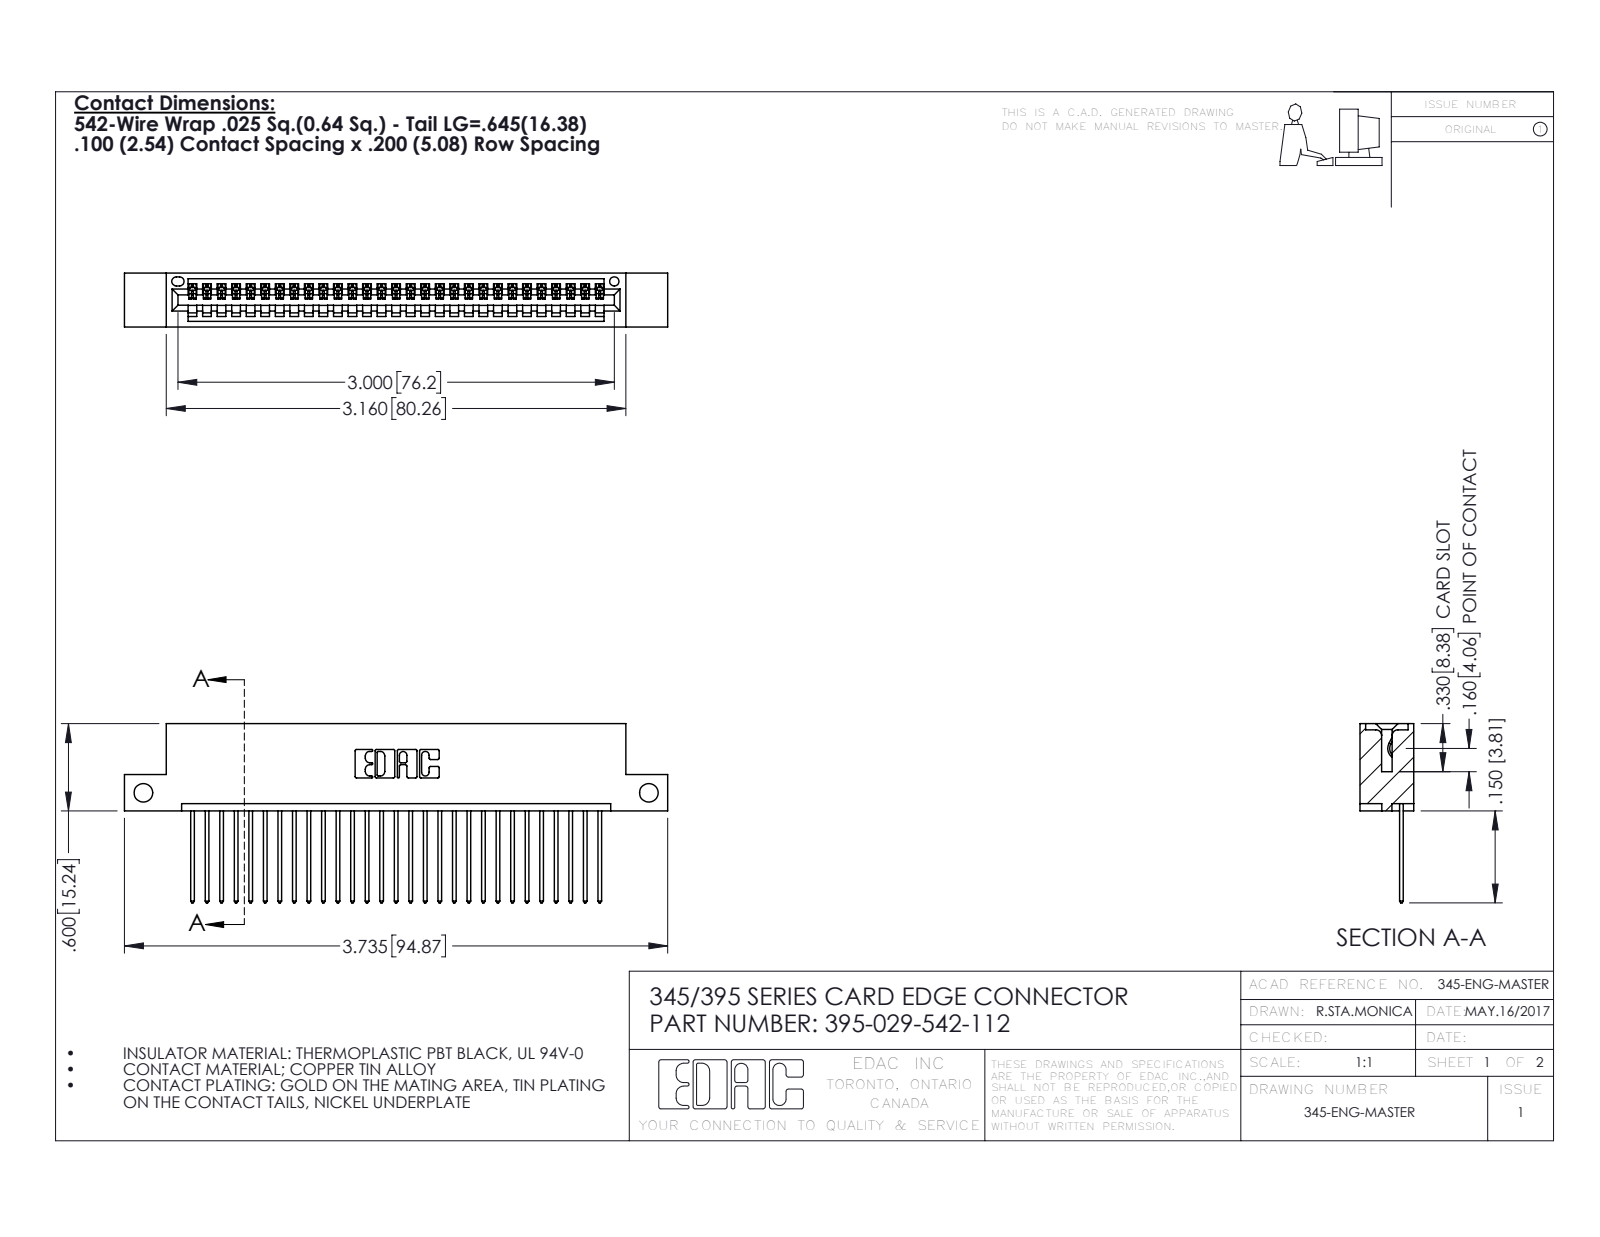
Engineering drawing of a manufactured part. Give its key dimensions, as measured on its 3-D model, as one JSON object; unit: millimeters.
{"part_name": "345 Part_Flush Mounting Lugs - Side Mount; 395-029-542-112; 345-292-001_345-293-142", "step_written_by": "SolidWorks 2016 (CONFIG_CONTROL_DESIGN)", "units": "millimeters", "bodies": {"solids": 30, "faces": 1808, "planar": 1240, "cylindrical": 568, "other": 0}, "overall_size": [94.9, 31.3, 9.4], "volume_mm3": 8880, "surface_area_mm2": 11890, "round_holes": [[3.3, 2], [1.6, 1]], "partial_cylinders_radius": [[0.2, 58], [0.3, 58], [0.3, 22], [0.2, 6], [0.8, 6], [0.7, 3], [0.8, 2], [1, 2]], "face_to_face_distances": [7.6, 1.8, 5.1, 9.4, 2.5, 6.9, 0.6, 5.7, 3.8, 1.8], "hole_center_spacings": [88.3]}
